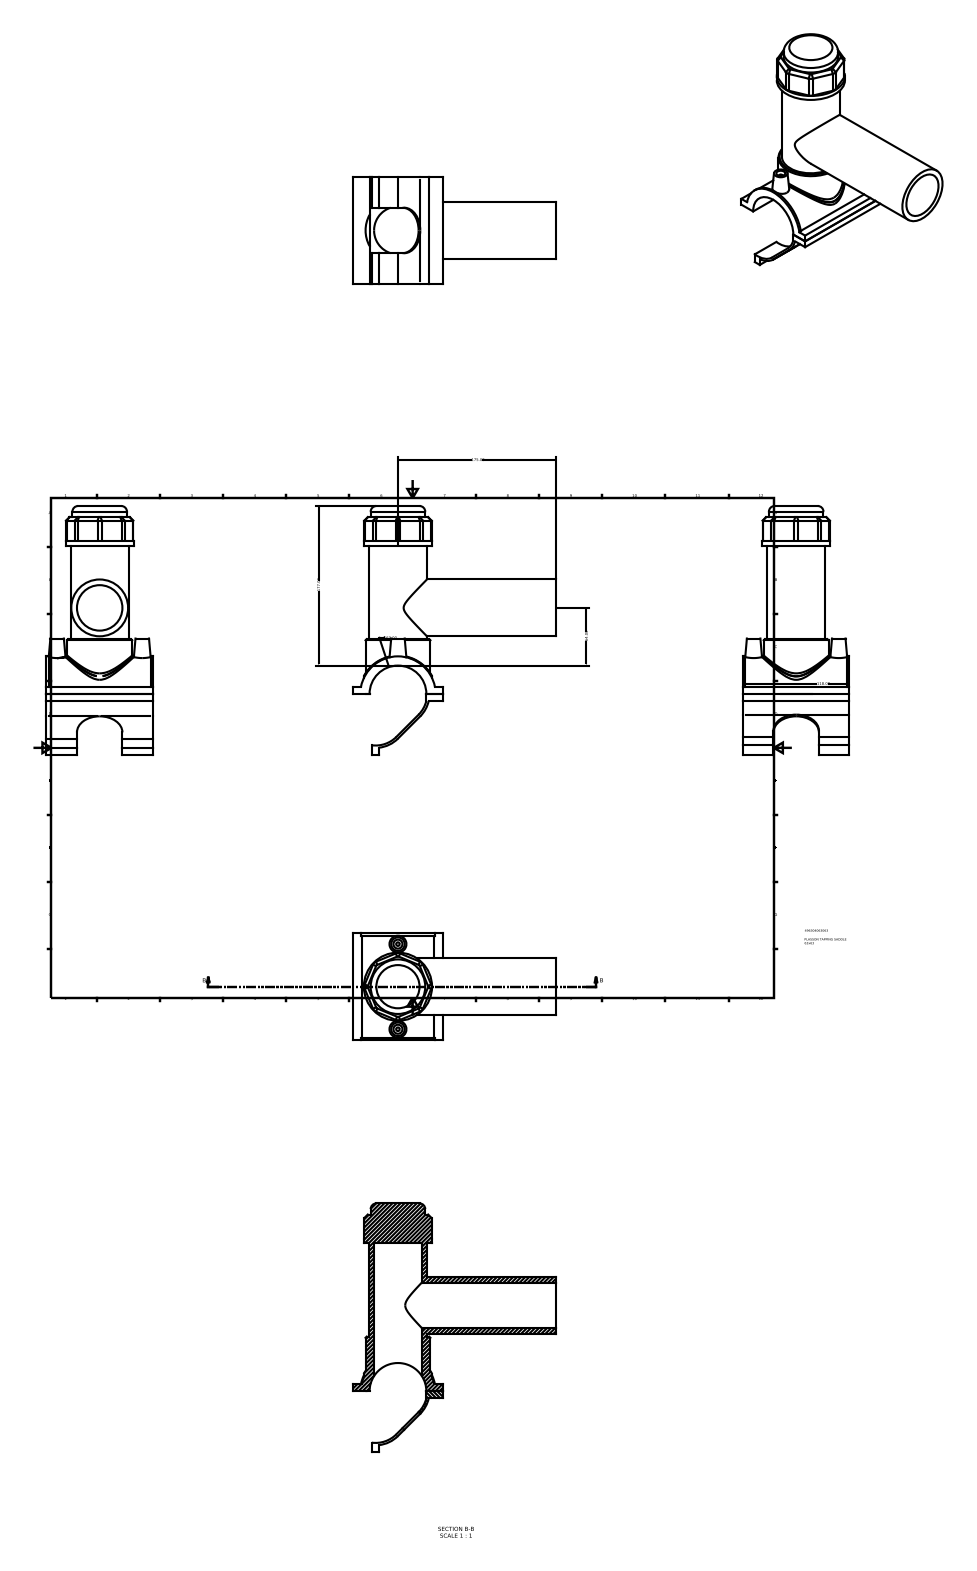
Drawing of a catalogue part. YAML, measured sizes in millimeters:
part_name: "496304063063"
step_written_by: "Autodesk Inventor 2015 (AUTOMOTIVE_DESIGN)"
units: millimeters
bodies: {solids: 2, faces: 106, planar: 59, cylindrical: 34, other: 13}
overall_size: [275.78, 225, 118]
volume: 646636
surface_area: 172727
round_holes:
  - {diameter: 10, count: 2}
  - {diameter: 50.4, count: 1}
  - {diameter: 52.92, count: 1}
round_bosses_or_shafts:
  - {diameter: 4, count: 2}
  - {diameter: 75.6, count: 1}
  - {diameter: 71.82, count: 1}
  - {diameter: 64.26, count: 1}
  - {diameter: 63, count: 1}
  - {diameter: 60.48, count: 1}
partial_cylinders:
  - {radius: 6.3, count: 8}
  - {radius: 32.38, count: 2}
  - {radius: 34.98, count: 2}
  - {radius: 25.2, count: 1}
  - {radius: 31.5, count: 1}
  - {radius: 40.95, count: 1}
  - {radius: 41.77, count: 1}
  - {radius: 42.59, count: 1}
face_to_face_distances: [164.2, 7.82, 2.6, 69.86, 172.02, 216.27, 208.45, 44.25, 118, 7.83]
hole_center_spacings: [47.2, 94.4]
